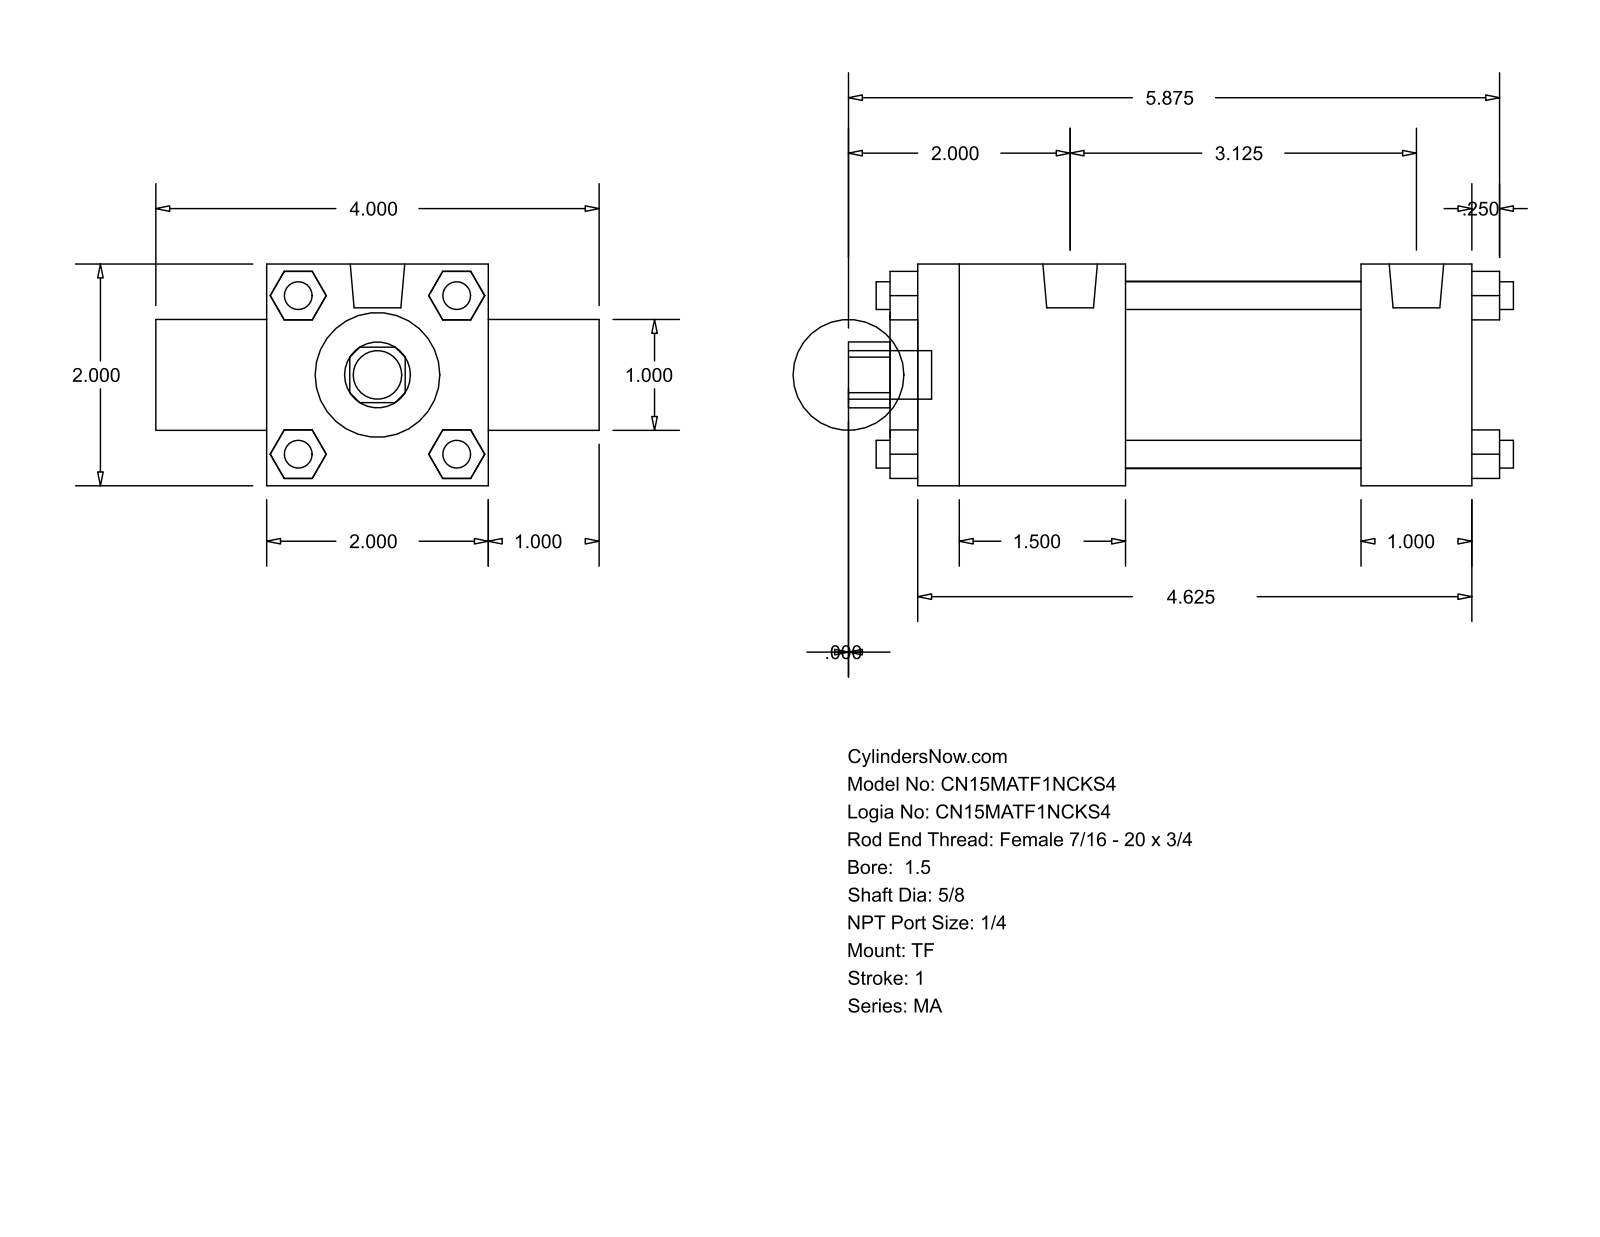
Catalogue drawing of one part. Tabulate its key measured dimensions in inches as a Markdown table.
| quantity | value |
| --- | --- |
| part name | MA_TF__0150_0.625 |
| STEP written by | GSSL Pune (CONFIG_CONTROL_DESIGN) |
| units | inches |
| bodies | 0 solids, 120 faces (92 planar, 28 cylindrical, 0 other) |
| overall size | 6 × 4 × 2 |
| round holes (diameter × count) | 0.625 × 1, 1 × 1, 1.125 × 1, 1.69 × 1 |
| round bosses / shafts (diameter × count) | 0.25 × 4, 0.313 × 3, 0.492 × 2, 0.437 × 1 |
| partial cylindrical surfaces (radius × count) | 0.297 × 1 |
| main face-to-face distances | 2, 2.125, 5, 1, 3, 1.875, 4, 3.125, 1, 5.25 |
